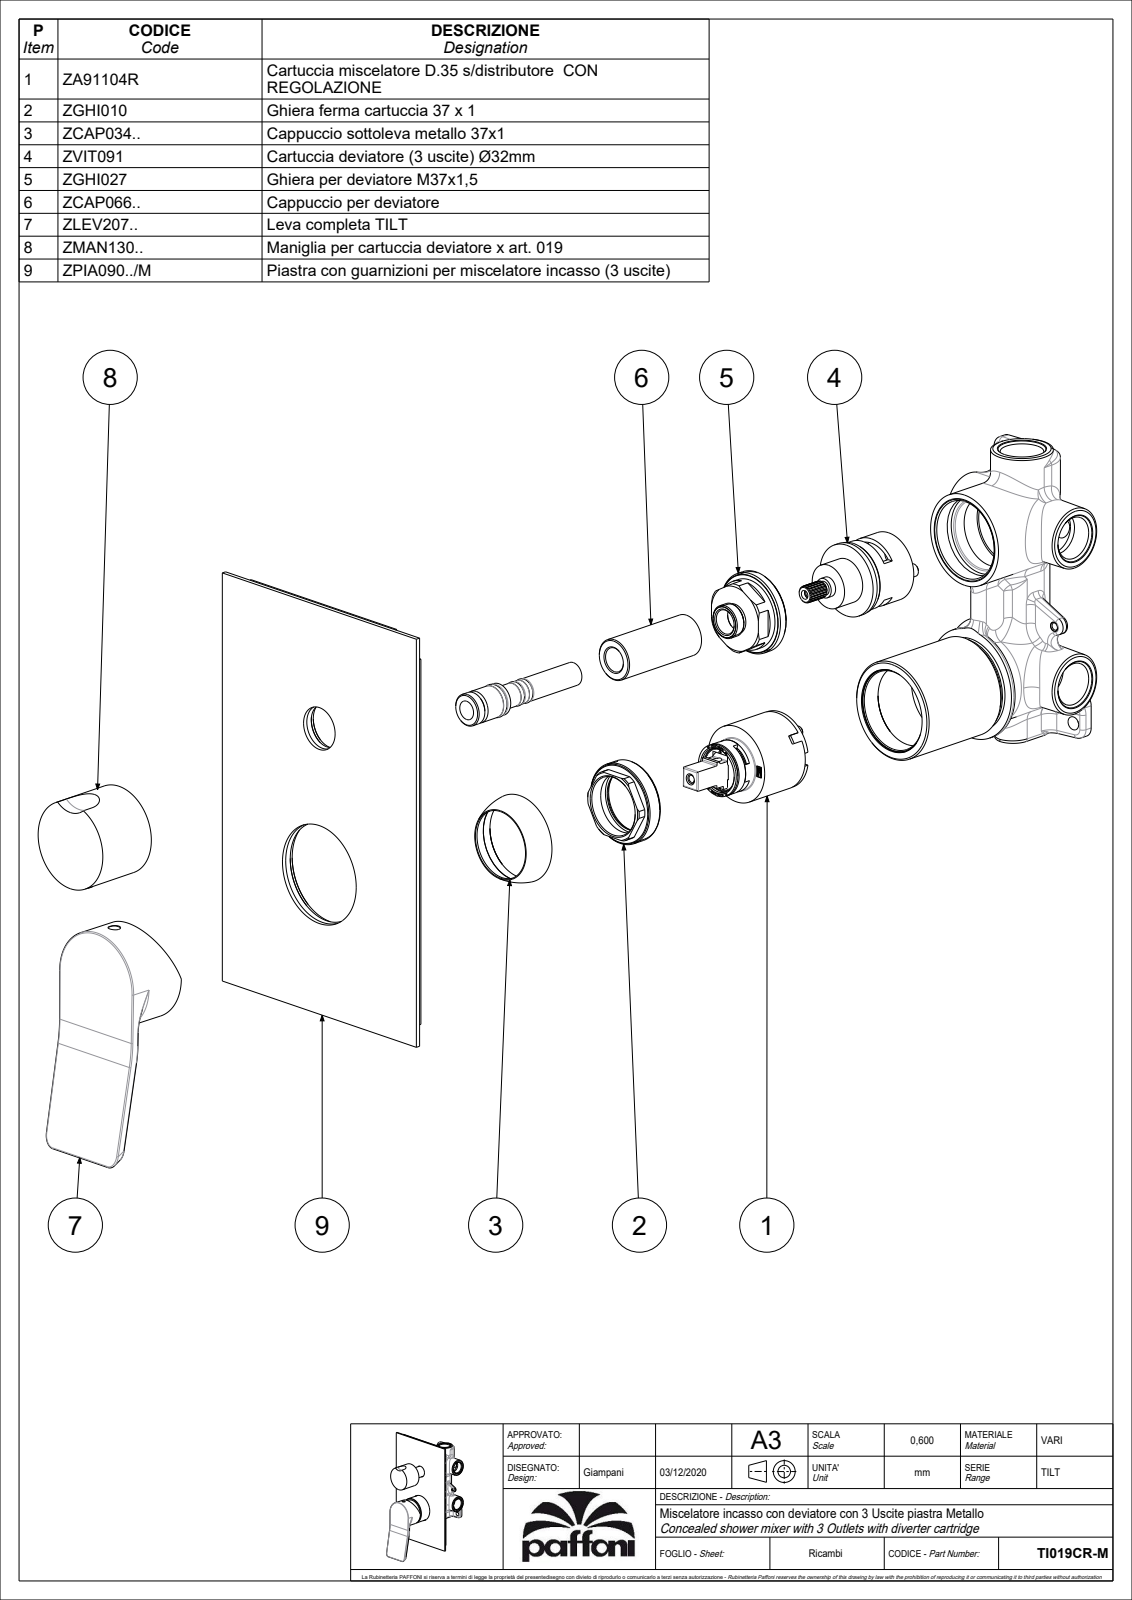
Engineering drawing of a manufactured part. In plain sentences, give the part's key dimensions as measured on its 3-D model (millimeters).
The part is named "TI019CR-M". Its 3-D file was written by "CREO PARAMETRIC BY PTC INC, 2020044 (CONFIG_CONTROL_DESIGN)". It is 2 solids with 213 faces: 72 planar, 79 cylindrical and 62 other. Overall it measures 204.58 by 120 by 64.05 millimeters. Its volume is 114 375 cubic millimeters and its surface area 85 378 square millimeters. Round holes: 2 of diameter 3, 2 of diameter 4.2, 2 of diameter 36, 1 of diameter 3.2, 1 of diameter 5.5, 1 of diameter 11, 1 of diameter 14.8, 1 of diameter 30.6, 1 of diameter 37.5. Round bosses or shafts: 1 of diameter 45.5, 1 of diameter 44.8, 1 of diameter 40, 1 of diameter 24, 1 of diameter 18.7, 1 of diameter 7.6, 1 of diameter 5.5. Partial cylindrical surfaces (rounded edges, fillets, slot ends): 10 of radius 0.5, 2 of radius 1.5, 2 of radius 5, 1 of radius 12.5, 1 of radius 44.14, 1 of radius 63. The main face-to-face distances are 2, 4.02, 55.1, 53.1, 4, 51.1, 49.1, 23.9, 25.9, 25.2. The hole center spacings are 1.8, 10, 68, 78.
